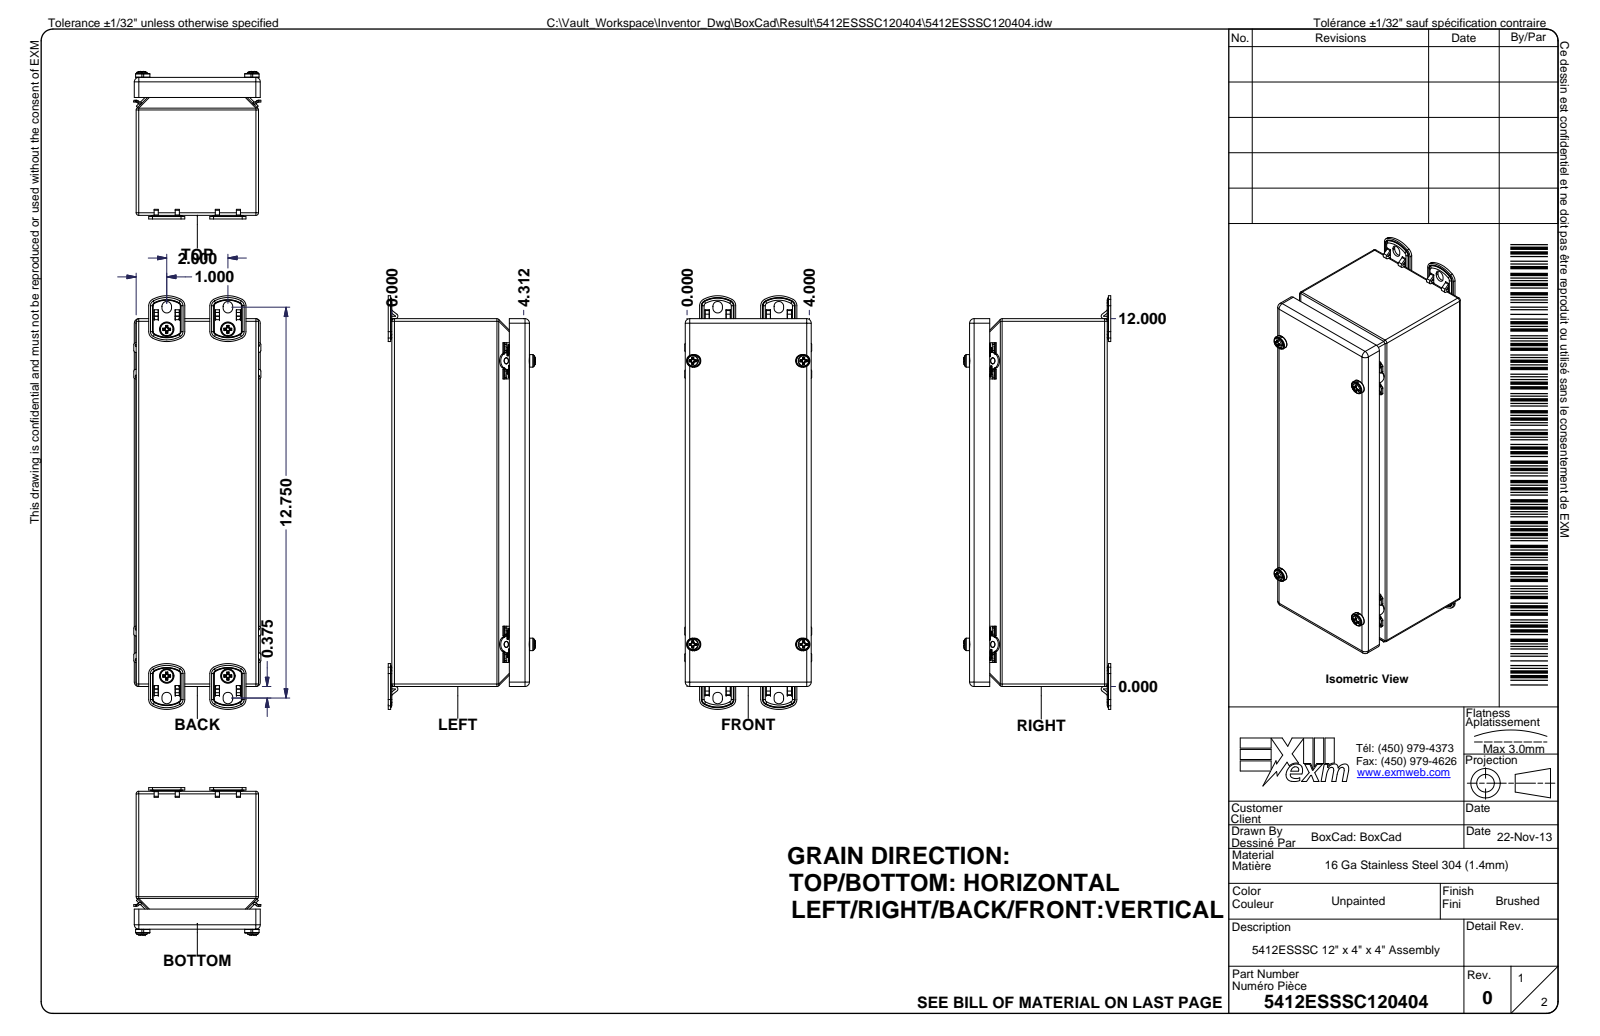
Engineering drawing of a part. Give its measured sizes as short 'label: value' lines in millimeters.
name: 5412ESSSC120404; 5412ESSSC120404B; 5412ESSSC120404B-P; RIVET_NUT_SS_M5_FH_OE (+8 more)
written by: Autodesk Inventor 2024 (AUTOMOTIVE_DESIGN)
unit: mm
bodies: 43 solids, 4475 faces (1992 planar, 1151 cylindrical, 1332 other)
size: 342.8 × 120.6 × 107.6
volume: 305 300 mm³; area: 435 000 mm²
holes: 6× ⌀5, 4× ⌀4, 4× ⌀5, 4× ⌀5, 4× ⌀6, 4× ⌀7, 3× ⌀8.1, 2× ⌀0.8, 2× ⌀5.1, 2× ⌀6.1
bosses: 8× ⌀5.9, 4× ⌀15, 4× ⌀12.7, 4× ⌀7, 4× ⌀6, 4× ⌀4.9, 4× ⌀3.5, 2× ⌀10
rounds: 224× R0.2, 82× R0.1, 60× R1, 48× R0.3, 48× R0.5, 32× R0.3, 28× R0.8, 24× R2.1
face distances: 1.3, 111.9, 100.3, 113.2, 110.5, 101.6, 98.9, 6, 7.7, 9.1
hole spacings: 75.8, 21.7, 76.2, 92.3, 248.3, 258.7, 13.9, 248.3
